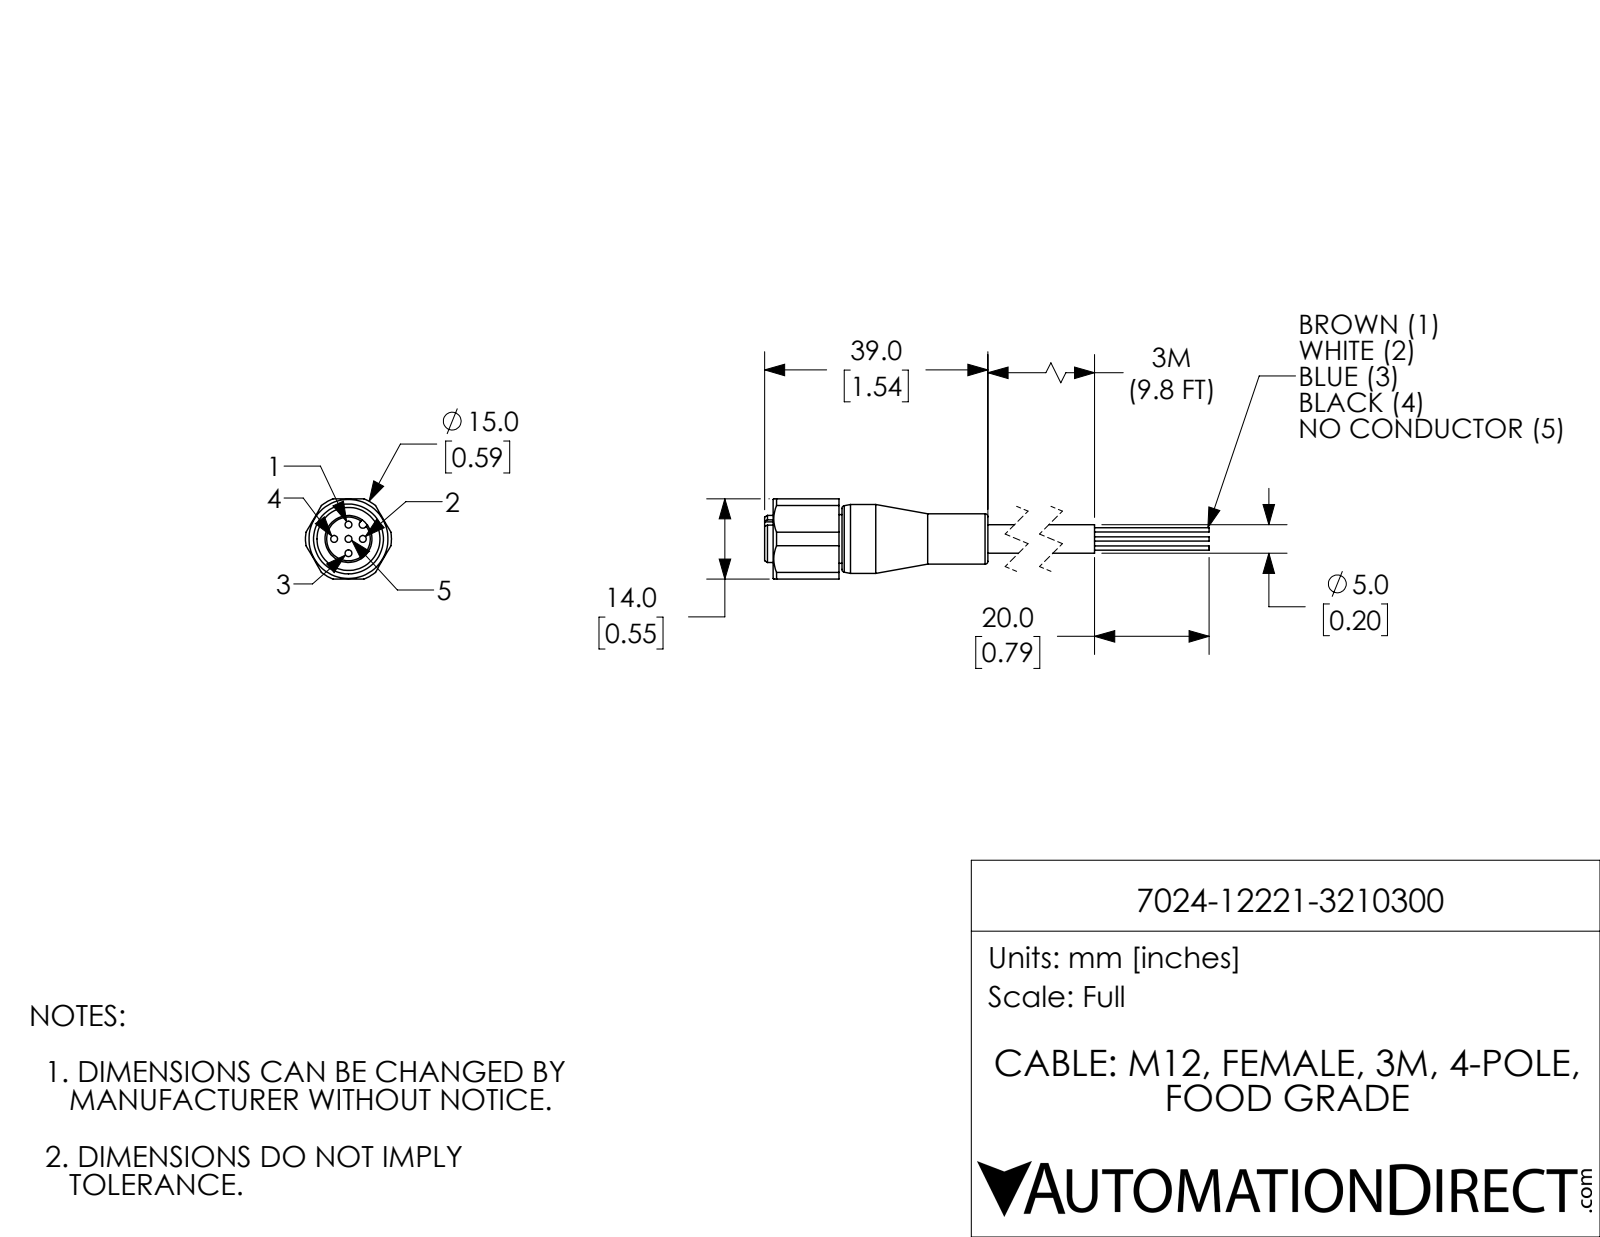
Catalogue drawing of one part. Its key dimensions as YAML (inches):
part_name: "7024-12221-3210300"
step_written_by: "SolidWorks 2018 (AUTOMOTIVE_DESIGN)"
units: inches
bodies: {solids: 1, faces: 77, planar: 25, cylindrical: 37, other: 15}
overall_size: [3.063, 0.591, 0.551]
volume: 0.251
surface_area: 4.383
round_holes:
  - {diameter: 0.047, count: 5}
  - {diameter: 0.433, count: 1}
round_bosses_or_shafts:
  - {diameter: 0.03, count: 4}
  - {diameter: 0.472, count: 1}
  - {diameter: 0.346, count: 1}
  - {diameter: 0.335, count: 1}
  - {diameter: 0.323, count: 1}
  - {diameter: 0.197, count: 1}
partial_cylinders:
  - {radius: 0.026, count: 1}
  - {radius: 0.295, count: 1}
face_to_face_distances: [0.551, 0.157, 0.354, 0.512, 0.059, 0.295, 0.453, 0.531, 0.472, 0.177]
hole_center_spacings: [0.098, 0.139, 0.197]
